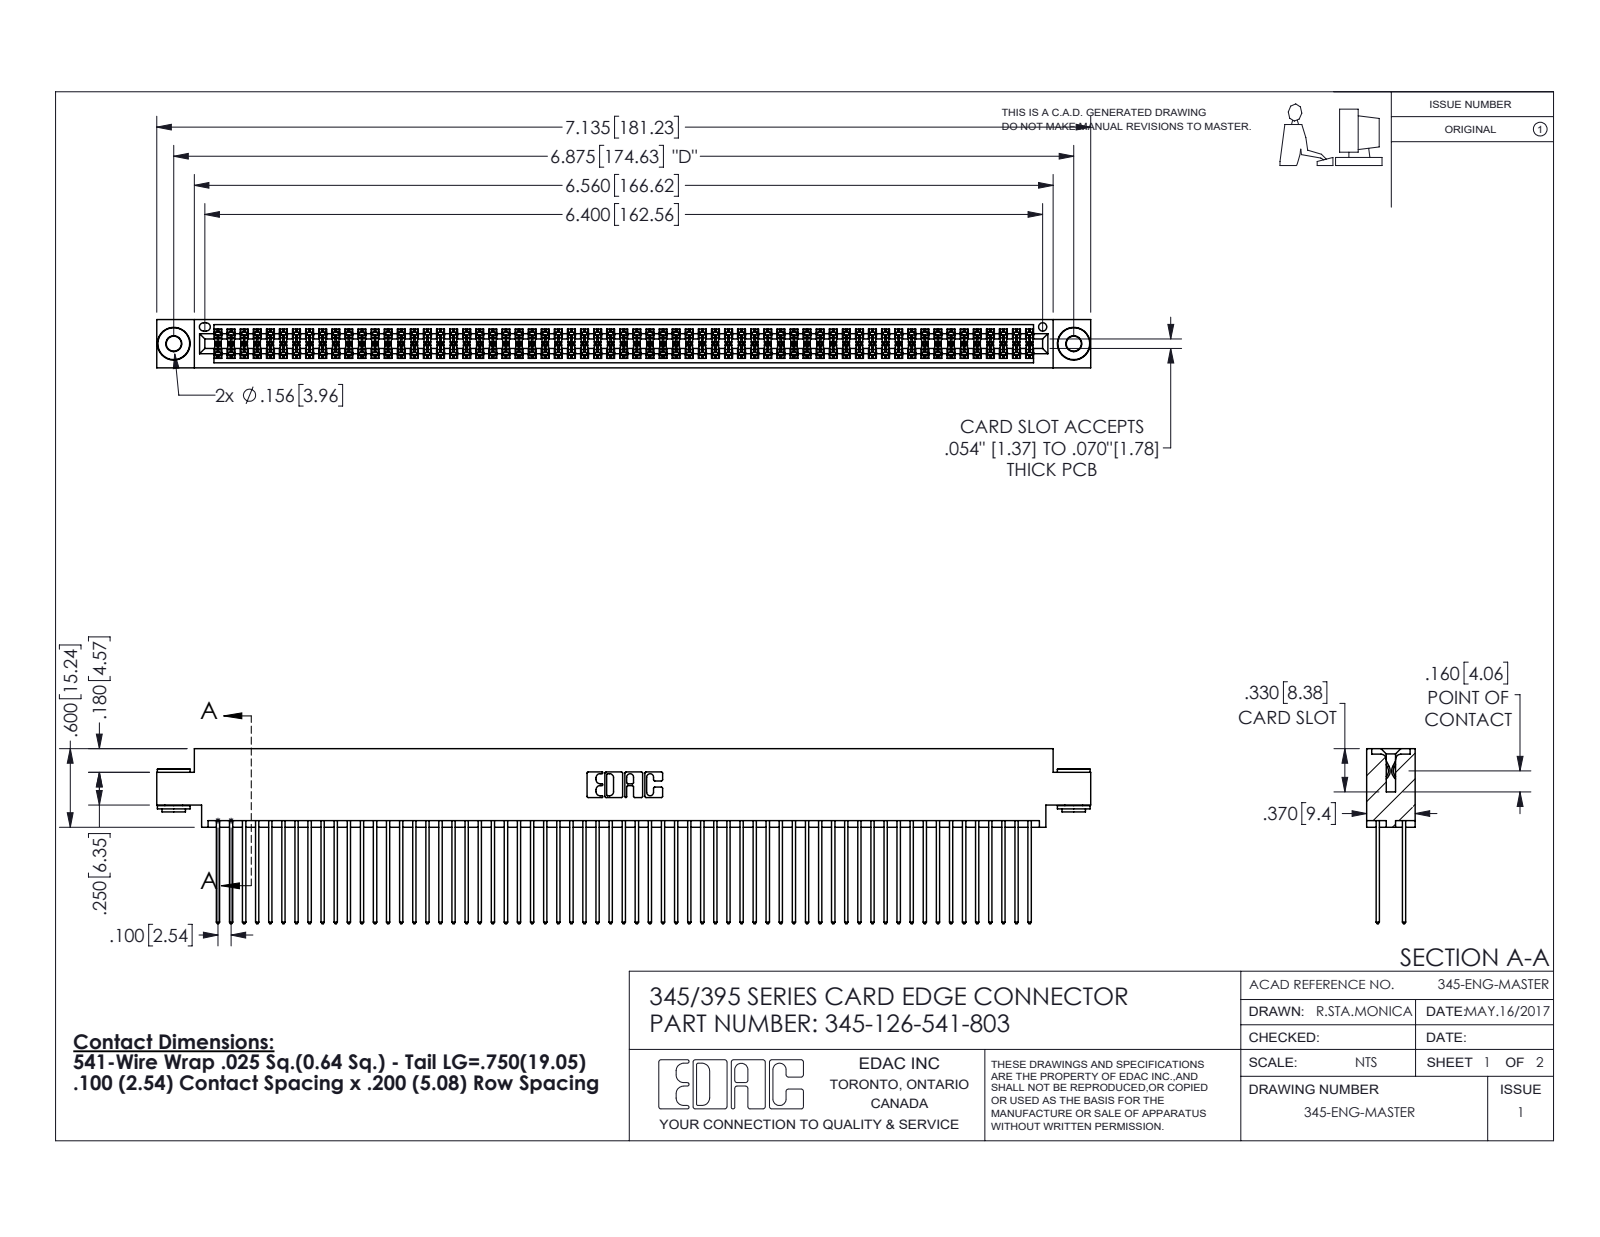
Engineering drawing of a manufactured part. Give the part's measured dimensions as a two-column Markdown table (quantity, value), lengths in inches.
| quantity | value |
| --- | --- |
| part name | 345-126-541-803; 345-250-002_345-250-002-102; 345-292-001_345-293-141; 345 Part_0.170 Offset - 0.156 Dia-TH |
| STEP written by | SolidWorks 2016 (CONFIG_CONTROL_DESIGN) |
| units | inches |
| bodies | 129 solids, 6468 faces (4252 planar, 2208 cylindrical, 8 other) |
| overall size | 7.135 × 1.337 × 0.37 |
| volume | 1.125 in³ |
| surface area | 48.66 in² |
| round holes (diameter × count) | 0.116 × 2, 0.156 × 2, 0.064 × 1 |
| round bosses / shafts (diameter × count) | 0.25 × 2, 0.18 × 2, 0.136 × 2 |
| partial cylindrical surfaces (radius × count) | 0.006 × 189, 0.01 × 126, 0.01 × 22, 0.007 × 6, 0.031 × 6, 0.026 × 3, 0.014 × 2, 0.019 × 2 |
| main face-to-face distances | 0.072, 0.298, 0.2, 0.098, 0.272, 0.025, 0.225, 0.37, 0.175, 0.149 |
| hole center spacings | 0.27, 6.639, 6.875 |
